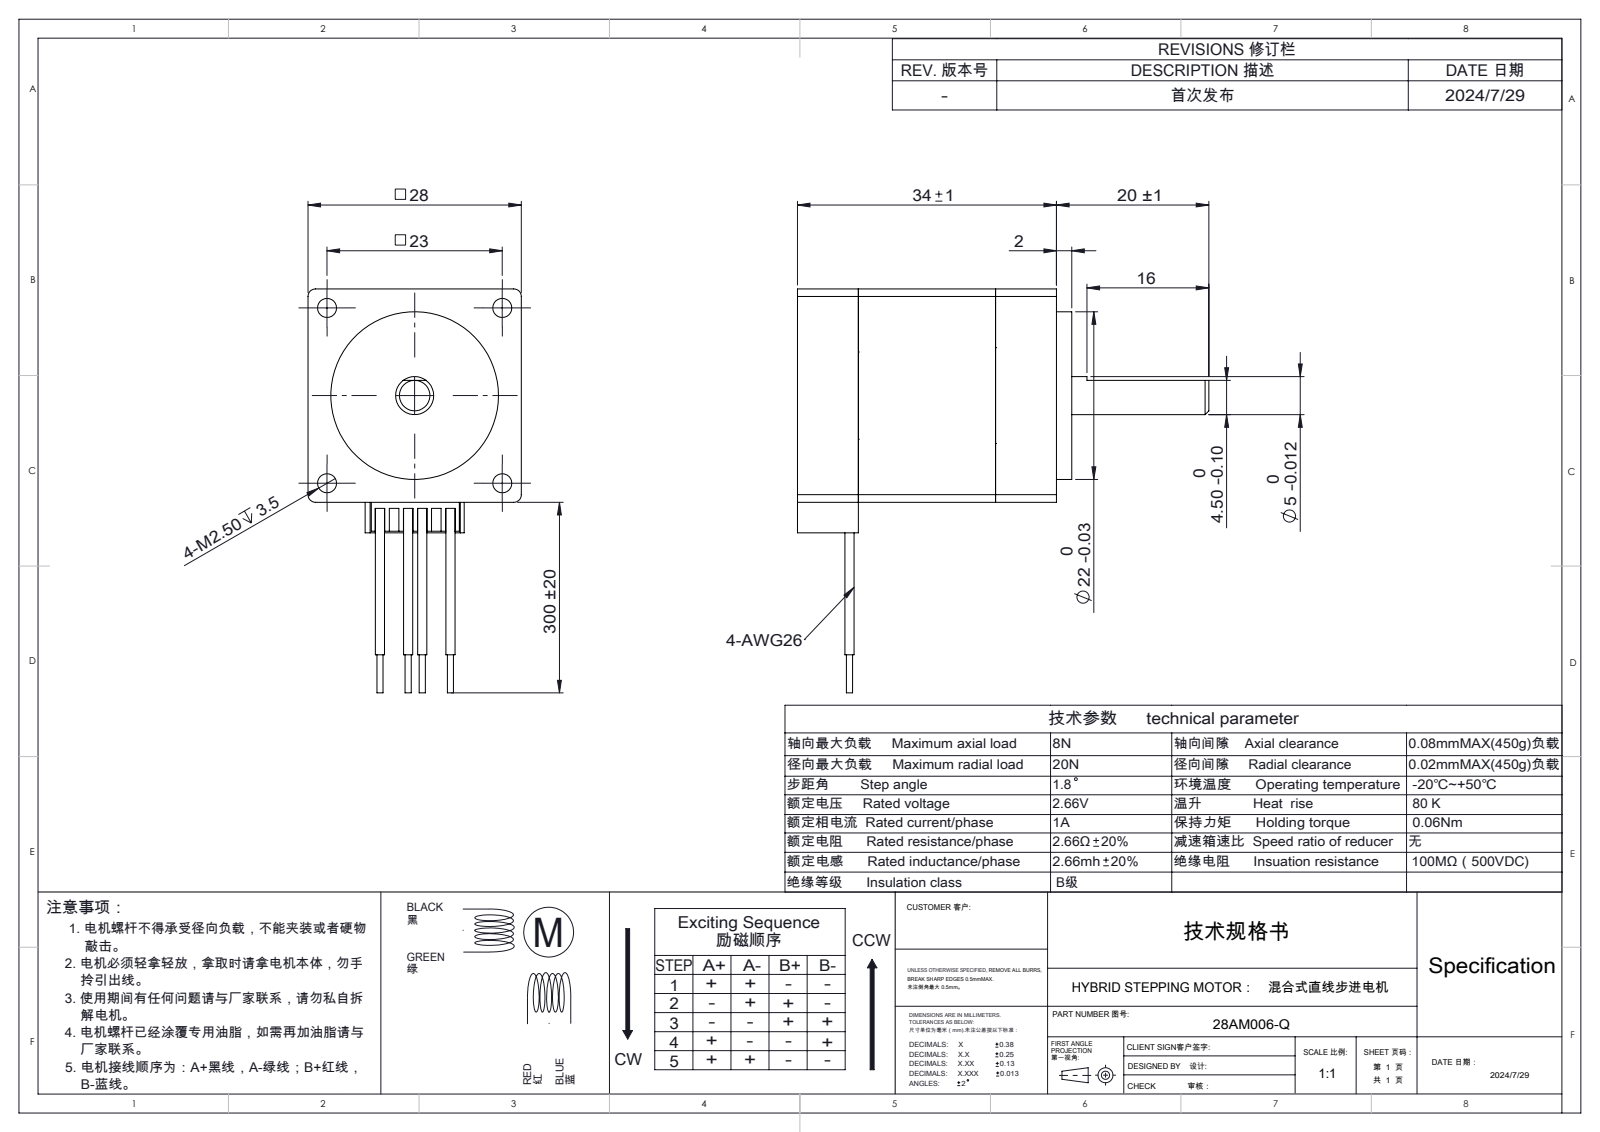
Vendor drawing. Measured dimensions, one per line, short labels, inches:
name: 28AM006-Q
written by: SolidWorks 2024 (AUTOMOTIVE_DESIGN)
unit: in
bodies: 2 solids, 137 faces (72 planar, 62 cylindrical, 3 other)
size: 2.126 × 2.087 × 1.102
volume: 1.637 in³; area: 16.58 in²
holes: 4× ⌀0.098, 1× ⌀0.197
bosses: 4× ⌀0.047, 4× ⌀0.031, 1× ⌀0.866, 1× ⌀0.494, 1× ⌀0.451
rounds: 4× R0.039
face distances: 1.102, 0.709, 0.315, 1.024, 1.339, 1.417, 0.079, 0.394, 0.073, 0.295
hole spacings: 0.64, 0.906, 1.281
